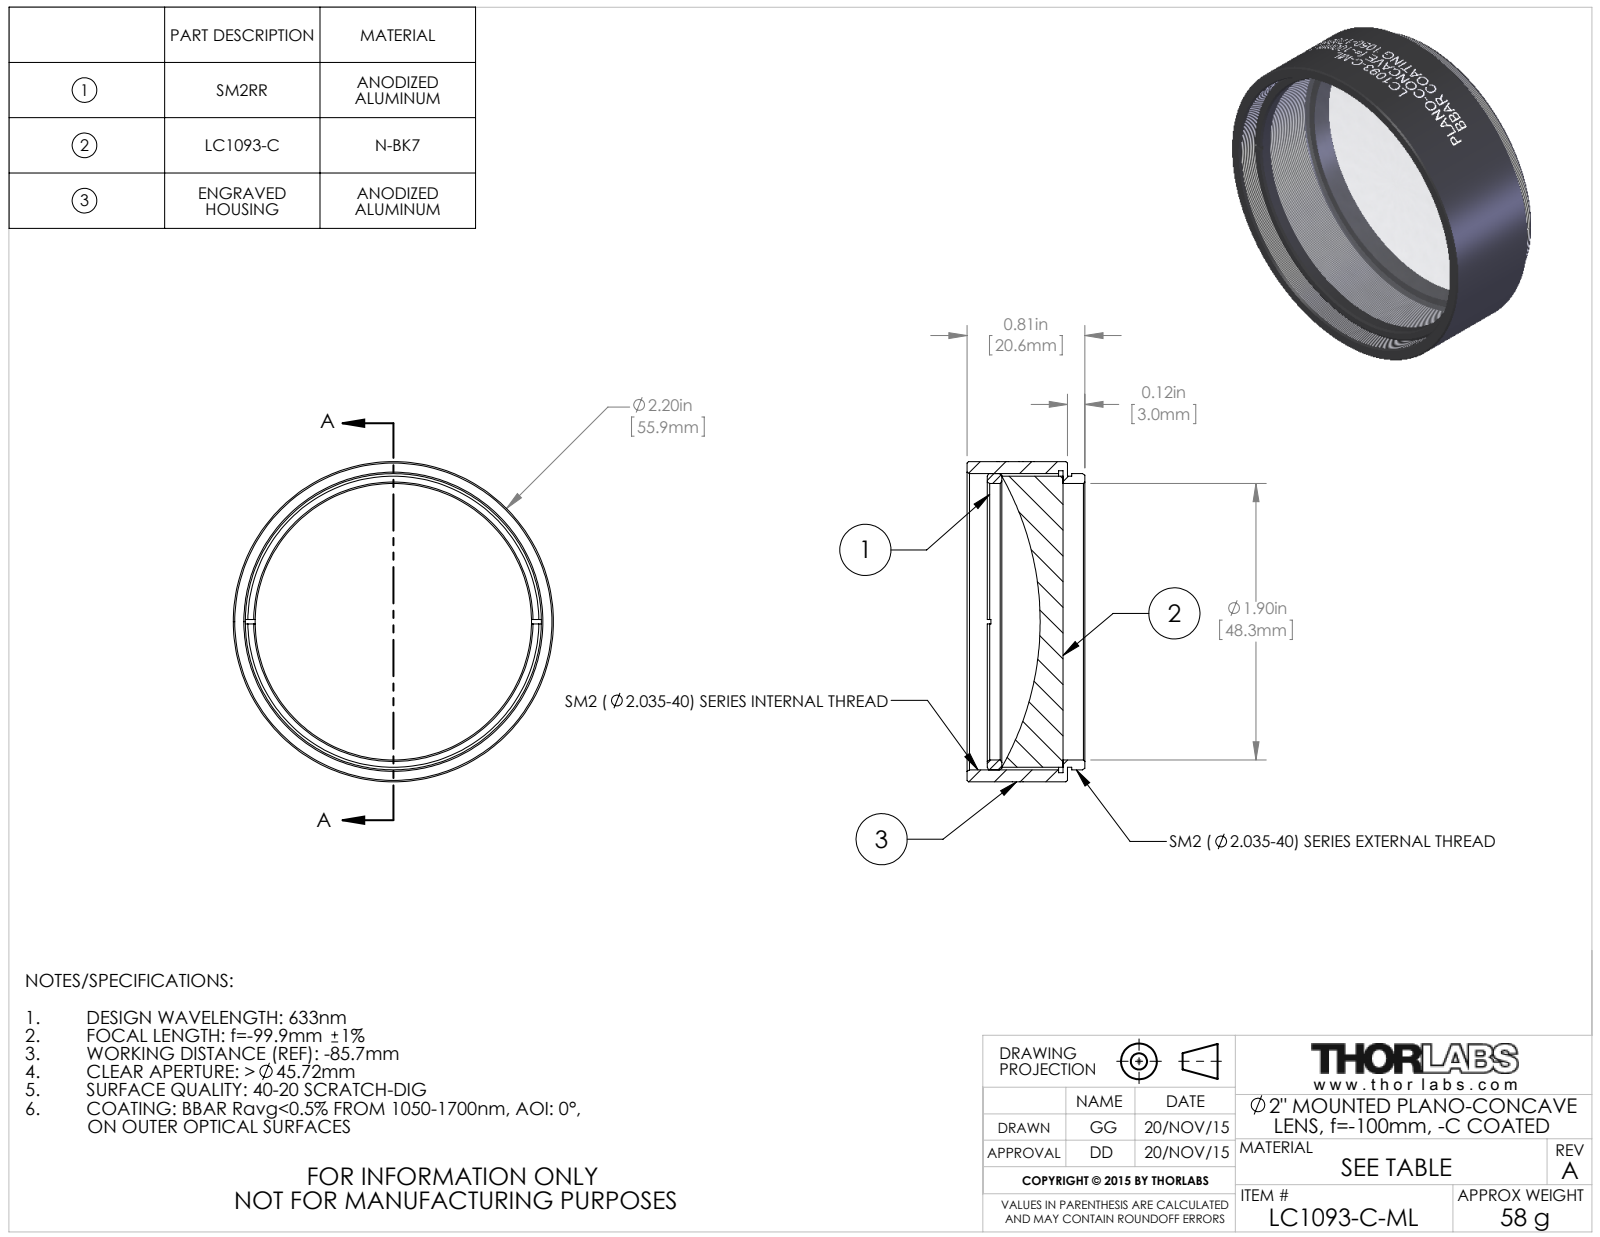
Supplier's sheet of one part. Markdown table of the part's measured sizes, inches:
| quantity | value |
| --- | --- |
| part name | TTN045358-E0W |
| STEP written by | SolidWorks 2014 (CONFIG_CONTROL_DESIGN) |
| units | inches |
| bodies | 3 solids, 149 faces (16 planar, 111 cylindrical, 22 other) |
| overall size | 2.2 × 2.2 × 0.81 |
| volume | 1.371 in³ |
| surface area | 23.9 in² |
| round holes (diameter × count) | 1.9 × 1, 2.075 × 1 |
| round bosses / shafts (diameter × count) | 2.2 × 1, 2.035 × 1, 2 × 1, 1.999 × 1 |
| main face-to-face distances | 0.03, 0.69, 0.66, 0.12, 0.15, 0.81, 0.572, 0.452, 0.422, 0.239 |
